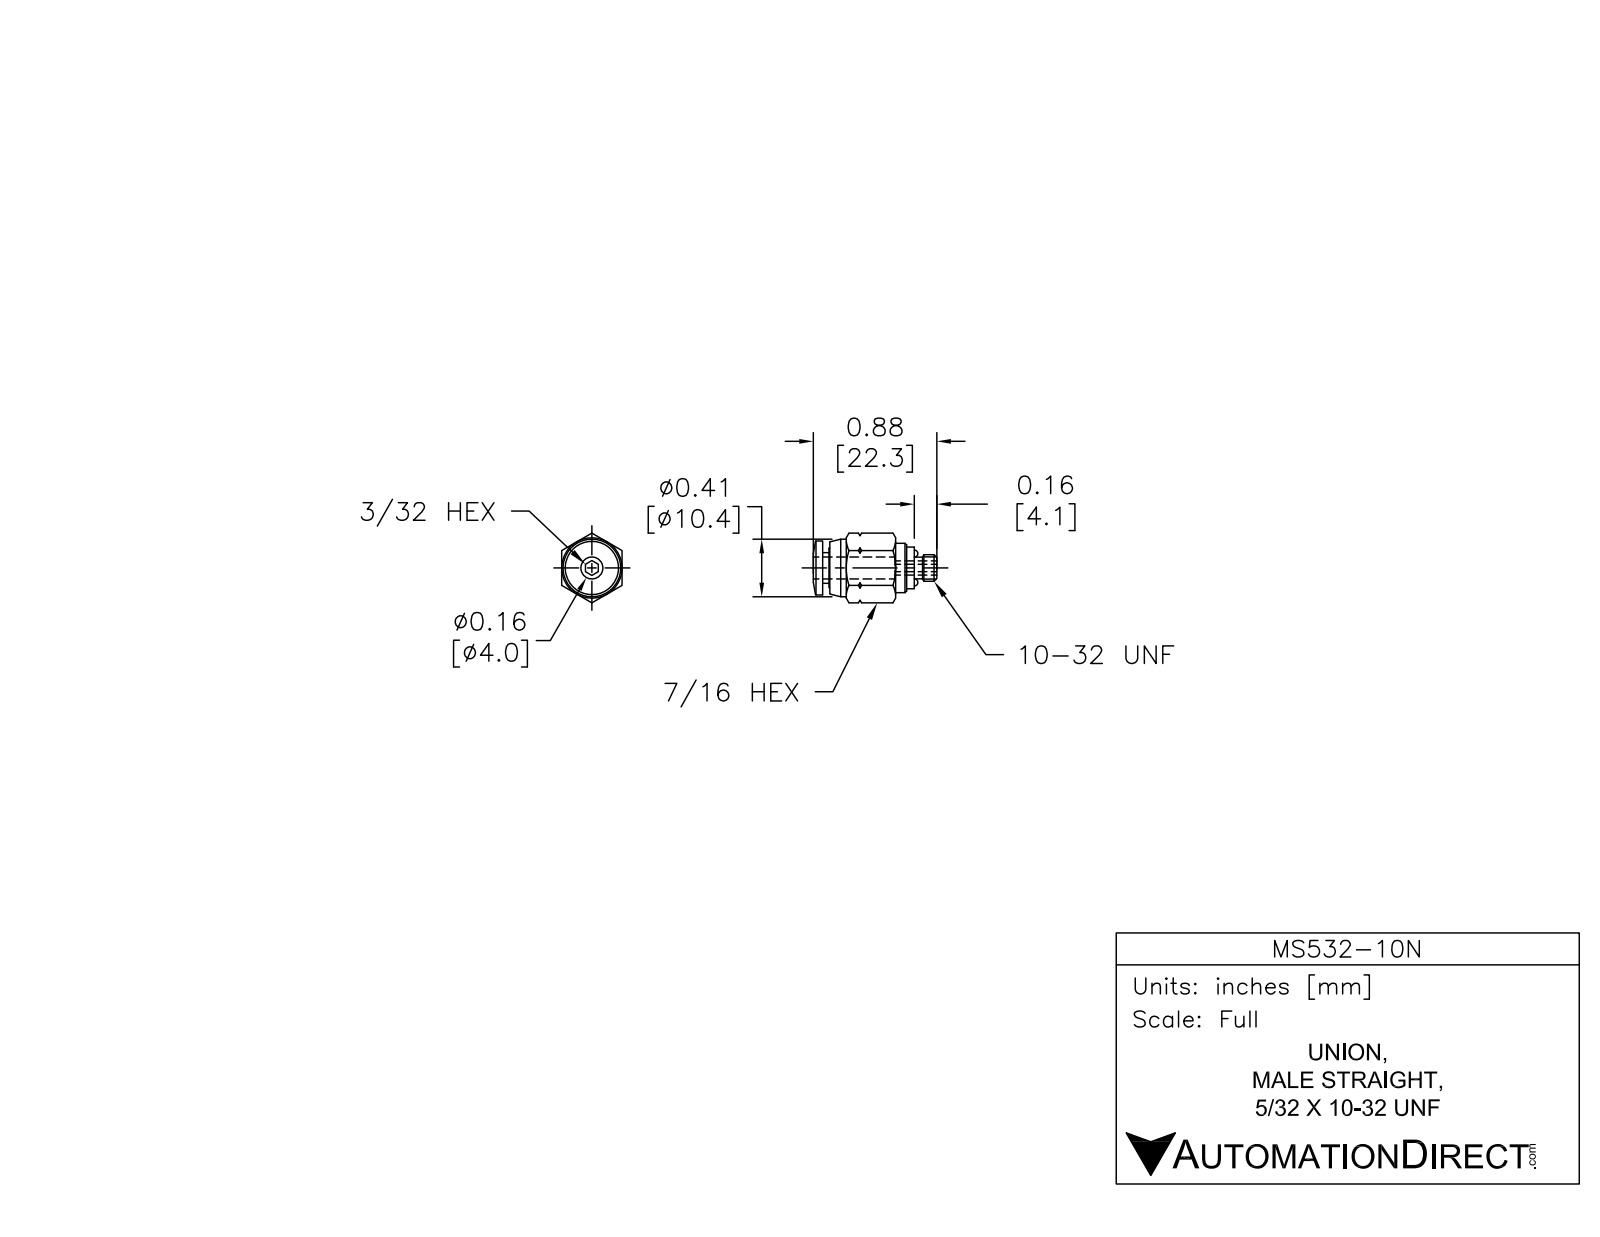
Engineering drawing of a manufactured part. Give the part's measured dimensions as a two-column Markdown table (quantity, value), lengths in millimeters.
| quantity | value |
| --- | --- |
| part name | PC5-32--U10 |
| STEP written by | Autodesk Inventor 2008 (AUTOMOTIVE_DESIGN) |
| units | millimeters |
| bodies | 2 solids, 63 faces (17 planar, 11 cylindrical, 35 other) |
| overall size | 22.5 × 12.7 × 11 |
| volume | 1 339 mm³ |
| surface area | 1 276 mm² |
| round holes (diameter × count) | 2.5 × 1, 4.3 × 1 |
| round bosses / shafts (diameter × count) | 10.5 × 1, 9.85 × 1, 9 × 1, 7.6 × 1, 7.2 × 1, 5.6 × 1, 4.83 × 1, 3.95 × 1 |
| main face-to-face distances | 11, 13.3, 12, 1.3, 2.6, 14.6, 15.9, 14.75, 12.15, 1.15 |
